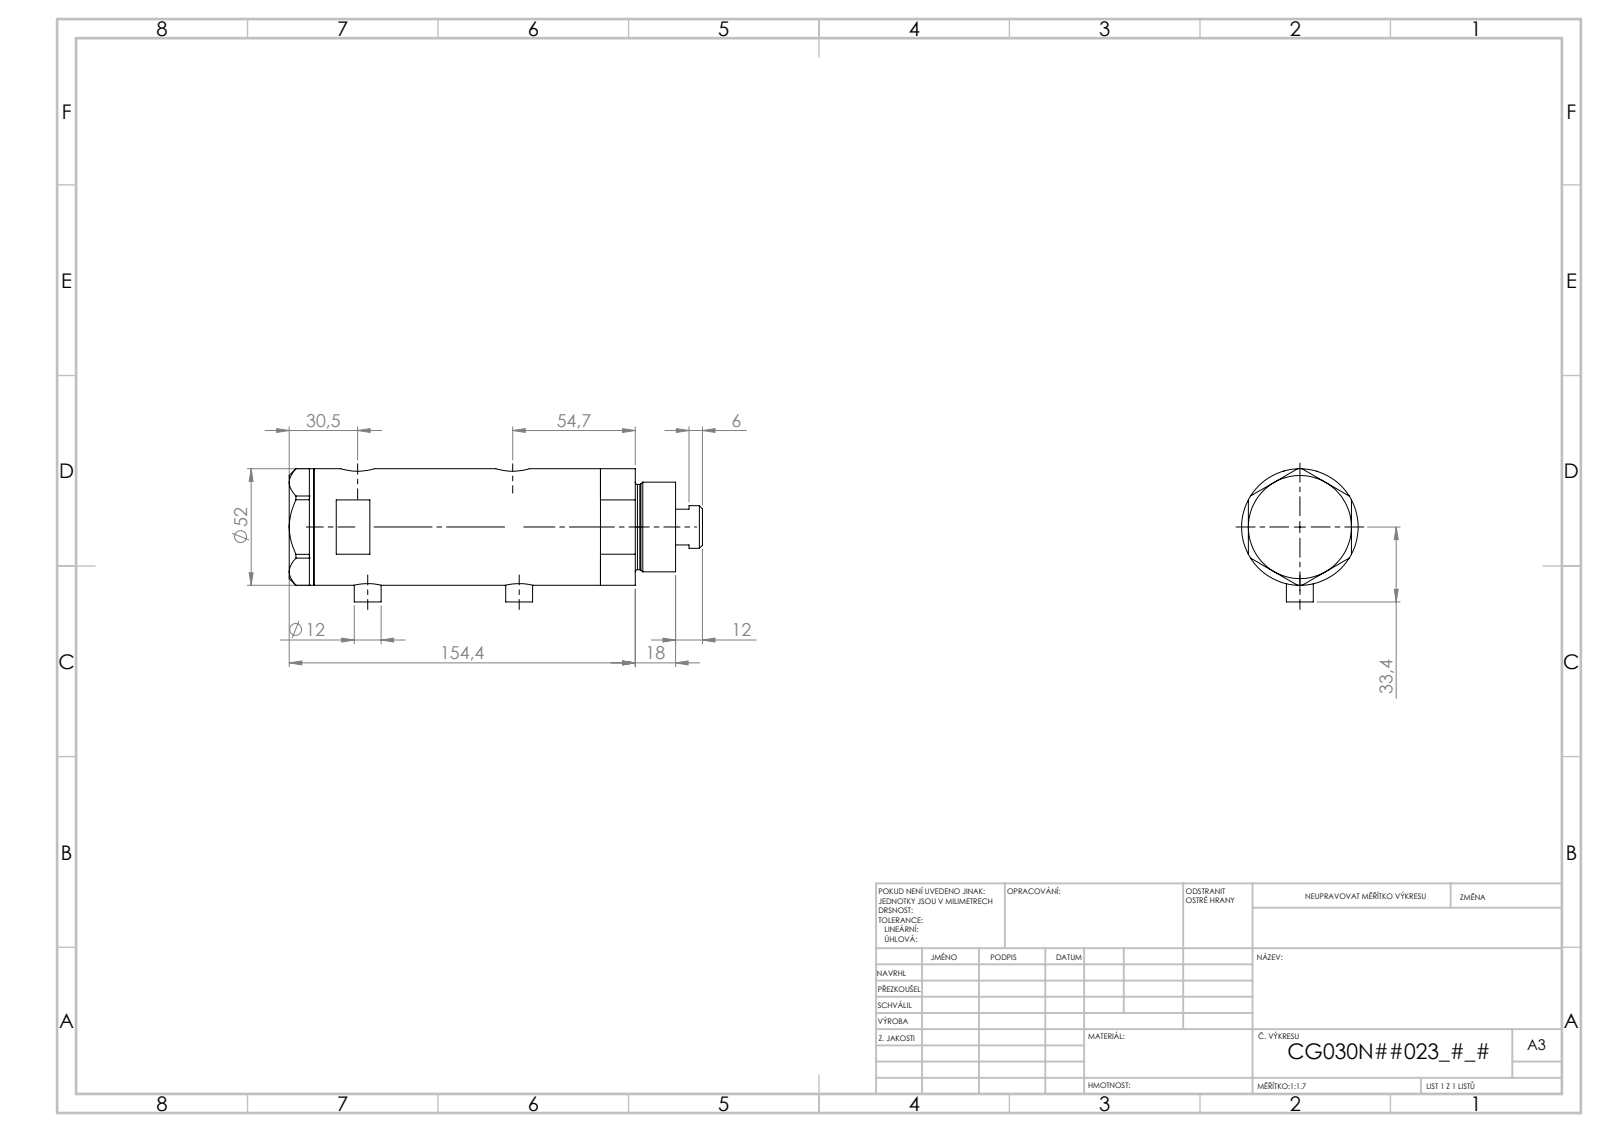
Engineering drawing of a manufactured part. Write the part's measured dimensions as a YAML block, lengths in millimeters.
part_name: "V270CG_FRONT; V270CG_BACK; V270CG_MIDDLE; V270CG_VC"
step_written_by: "SolidWorks 2019 (CONFIG_CONTROL_DESIGN)"
units: millimeters
bodies: {solids: 4, faces: 140, planar: 67, cylindrical: 53, other: 20}
overall_size: [172.02, 53.1, 52]
volume: 307332
surface_area: 72460
round_holes:
  - {diameter: 5, count: 2}
  - {diameter: 9.73, count: 2}
  - {diameter: 12.5, count: 2}
  - {diameter: 15, count: 2}
  - {diameter: 6.5, count: 1}
  - {diameter: 20, count: 1}
  - {diameter: 21.5, count: 1}
  - {diameter: 30, count: 1}
  - {diameter: 33, count: 1}
  - {diameter: 44, count: 1}
round_bosses_or_shafts:
  - {diameter: 12, count: 2}
  - {diameter: 52, count: 1}
  - {diameter: 40, count: 1}
  - {diameter: 38, count: 1}
  - {diameter: 19, count: 1}
face_to_face_distances: [76.56, 23.8, 52.76, 11, 34.8, 87.56, 46, 123.96, 112.96, 89.16]
hole_center_spacings: [2.9, 4.5, 49.75, 52.65, 54.25, 57.15, 2.89, 2.91]
